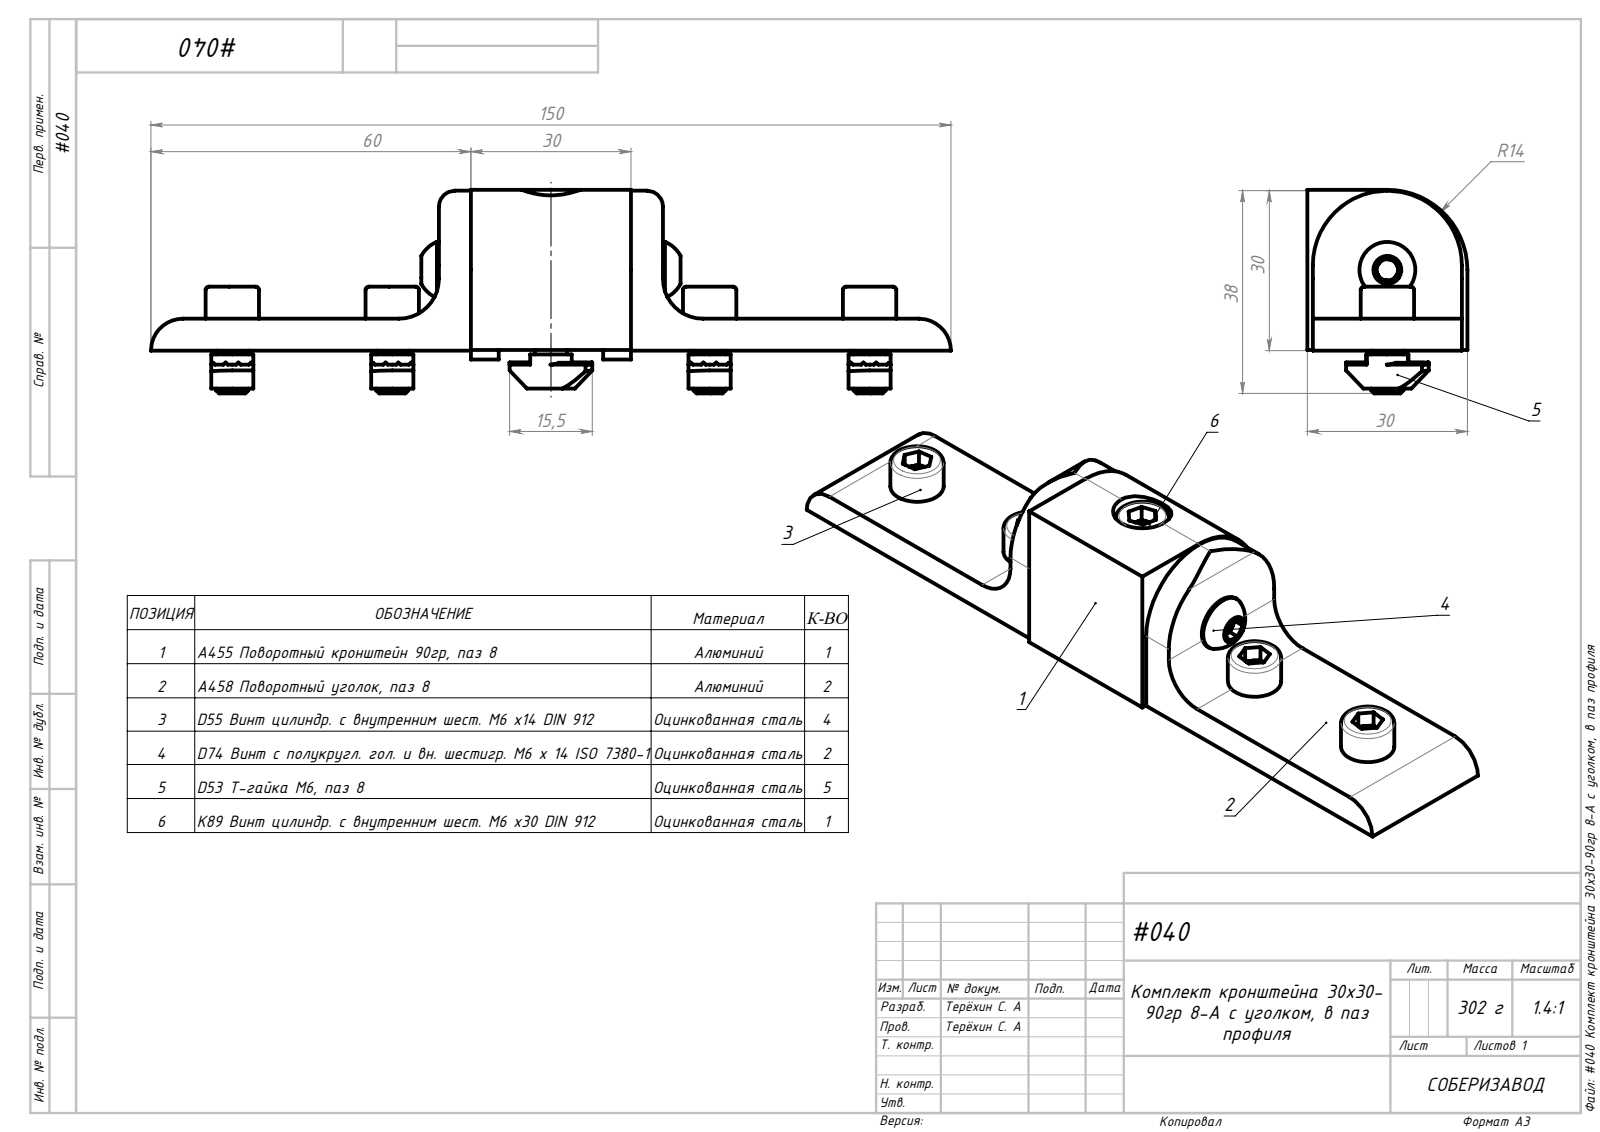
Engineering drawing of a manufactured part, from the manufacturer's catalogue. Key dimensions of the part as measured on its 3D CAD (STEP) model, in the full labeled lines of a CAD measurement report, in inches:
Part name (STEP PRODUCT): A458 Поворотный уголок, паз 8; K89 Винт цилиндр. с внутренним шест. М6 х30 DIN 912; #040 Комплект кронштейна 30х30-90гр с уголком, в паз профиля; D74 Винт с полукругл. гол. и вн. шестигр. М6 х 14 ISO 7380-1 (+4 more)
STEP written by: SolidWorks 2021 (AUTOMOTIVE_DESIGN)
Units: inches
Bodies: 16 solids, 753 faces (406 planar, 227 cylindrical, 120 other)
Overall size (bounding box): 5.906 × 5.906 × 2.362
Volume: 6.007 in³ · Surface area: 121.6 in²
Round holes (diameter × count): ⌀0.197 ×5, ⌀0.248 ×5, ⌀0.181 ×4, ⌀0.201 ×1, ⌀0.246 ×1, ⌀0.433 ×1
Round bosses / shafts (diameter × count): ⌀0.236 ×6, ⌀0.394 ×5, ⌀0.413 ×1
Partial cylindrical surfaces — rounded edges, fillets, slot ends (radius × count): R0.01 ×72, R0.03 ×16, R0.157 ×10, R0.27 ×10, R0.008 ×8, R0.02 ×8, R0.079 ×4, R0.118 ×2
Main face-to-face distances: 1.181, 0.315, 0.866, 0.043, 0.272, 0.909, 0.594, 0.361, 0.09, 0.046
Hole centre spacings: 0.906, 1.171, 1.181, 1.281, 2.352, 3.524, 2.343, 4.705
